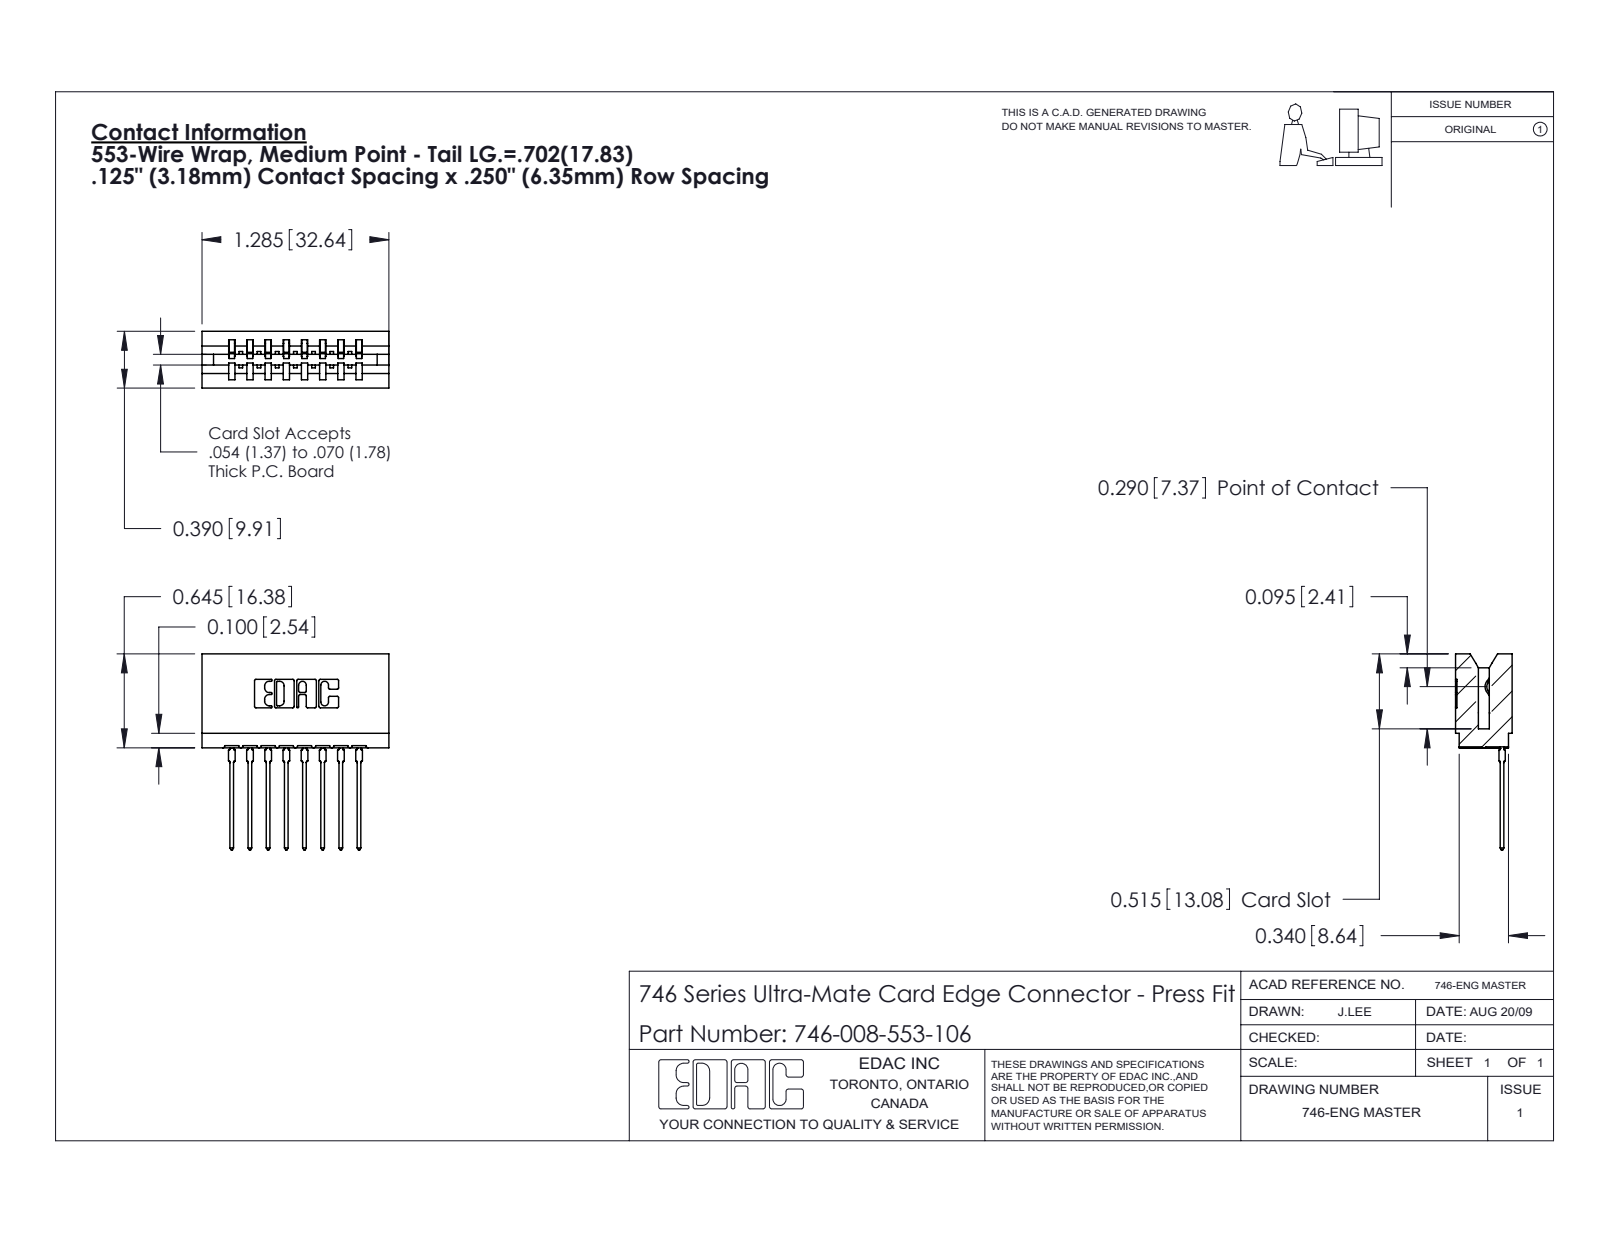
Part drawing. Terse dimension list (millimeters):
name: 746-008-553-106; 746 Part_.515 Slot Depth - 06; 746-292-001_553
written by: SolidWorks 2020 (CONFIG_CONTROL_DESIGN)
unit: mm
bodies: 9 solids, 962 faces (560 planar, 194 cylindrical, 208 other)
size: 34.2 × 32.6 × 9.9
volume: 3 650 mm³; area: 5 001 mm²
rounds: 22× R0.3, 16× R0.5, 9× R0.4, 6× R0.2, 6× R0.8, 4× R0.1, 4× R0.3, 3× R0.7
face distances: 6.4, 3.2, 12.7, 1.1, 8.5, 1.4, 7.4, 9.5, 5.3, 3.2
